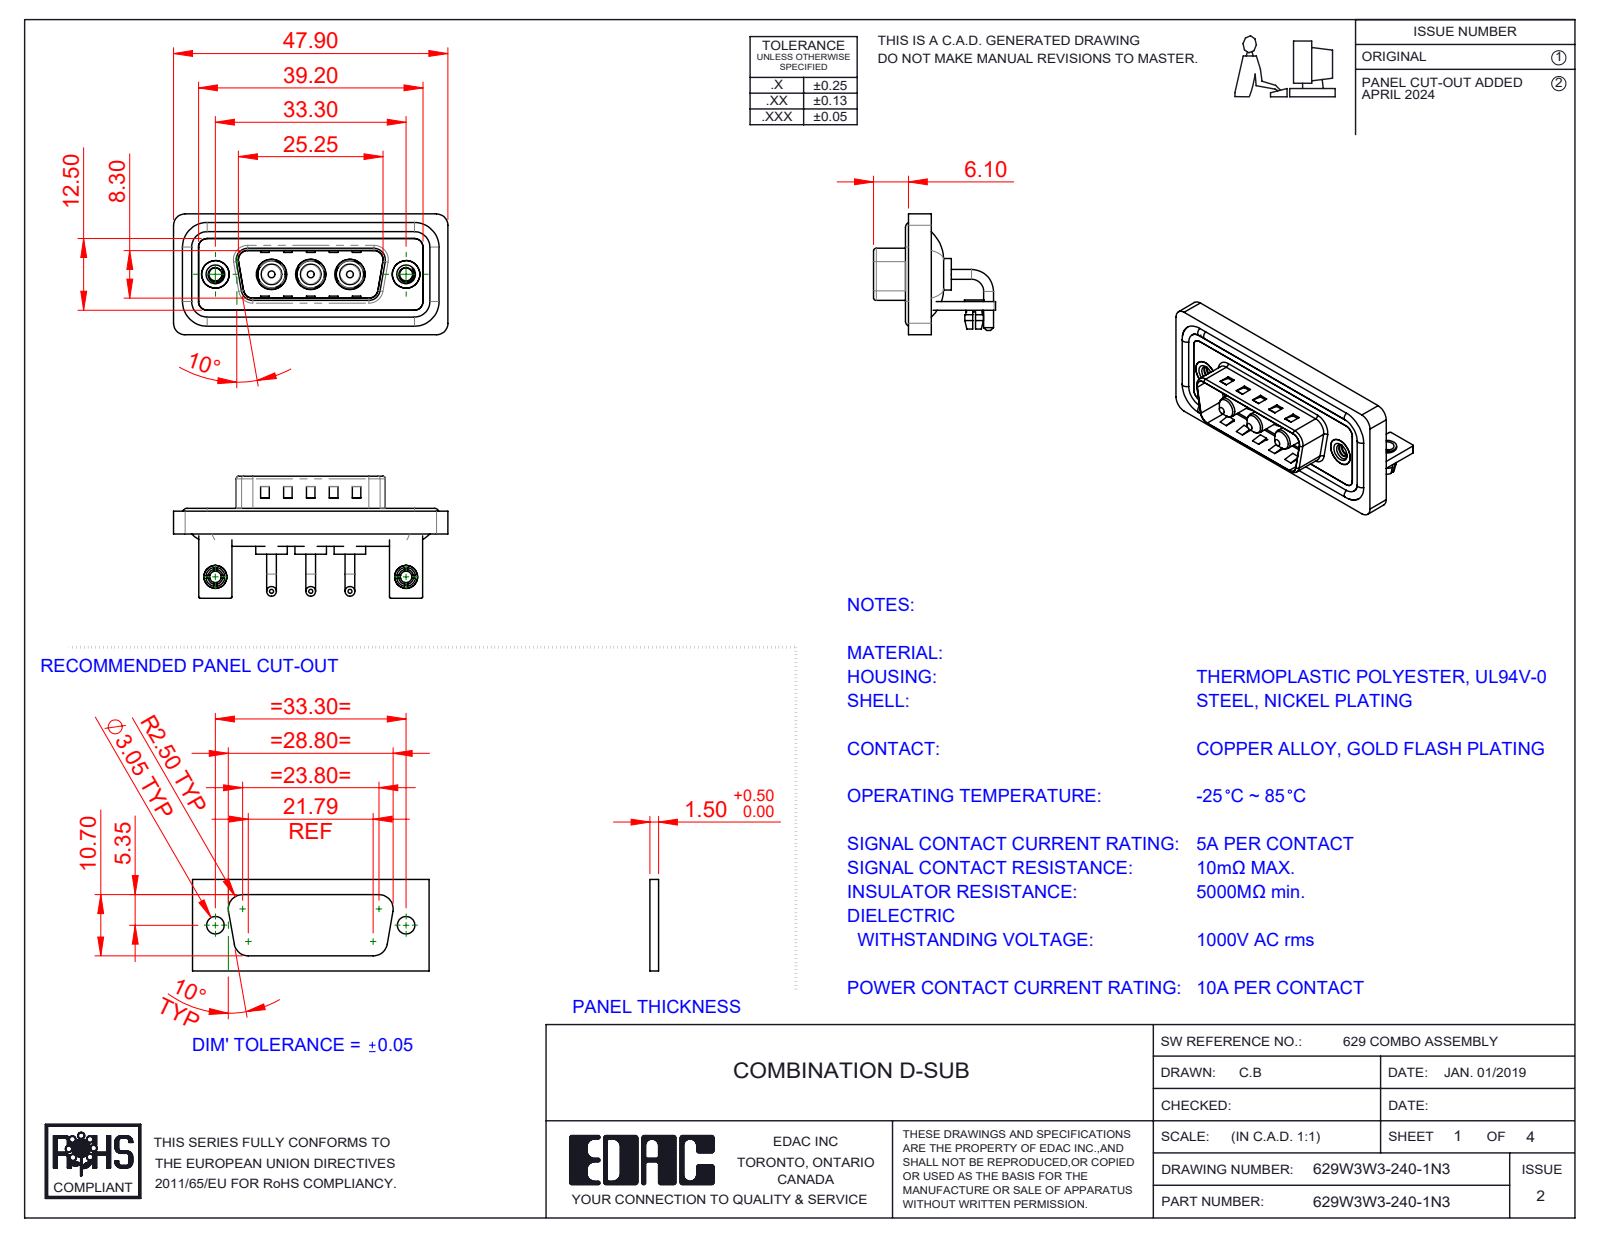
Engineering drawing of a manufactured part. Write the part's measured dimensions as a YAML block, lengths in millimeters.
part_name: "629Combo Shell Rear_15 Contacts; 629Combo Stabilizer Bracket; Power Pin_10A RA; 629Combo Board Lock (+5 more)"
step_written_by: "SolidWorks 2023 (CONFIG_CONTROL_DESIGN)"
units: millimeters
bodies: {solids: 17, faces: 708, planar: 275, cylindrical: 297, other: 136}
overall_size: [47.9, 21.3, 21.1]
volume: 5918
surface_area: 9681
round_holes:
  - {diameter: 4.85, count: 3}
  - {diameter: 5.3, count: 3}
  - {diameter: 2, count: 2}
  - {diameter: 2.26, count: 2}
  - {diameter: 2.5, count: 2}
  - {diameter: 3.2, count: 2}
  - {diameter: 4, count: 2}
  - {diameter: 4.8, count: 2}
  - {diameter: 5, count: 2}
round_bosses_or_shafts:
  - {diameter: 1.7, count: 6}
  - {diameter: 1.6, count: 4}
  - {diameter: 5.5, count: 3}
  - {diameter: 5.2, count: 3}
  - {diameter: 4.75, count: 3}
  - {diameter: 3.75, count: 3}
  - {diameter: 3.6, count: 3}
  - {diameter: 4.9, count: 2}
partial_cylinders:
  - {radius: 2, count: 21}
  - {radius: 1.5, count: 18}
  - {radius: 0.25, count: 16}
  - {radius: 0.5, count: 9}
  - {radius: 1.6, count: 8}
  - {radius: 0.6, count: 4}
  - {radius: 0.65, count: 4}
  - {radius: 0.9, count: 4}
face_to_face_distances: [0.4, 1.5, 0.8, 2.9, 1.1, 2.1, 3.7, 1.6, 1.2, 4.5]
hole_center_spacings: [6.85, 9.8, 16.65, 23.5, 33.3, 13.7]
